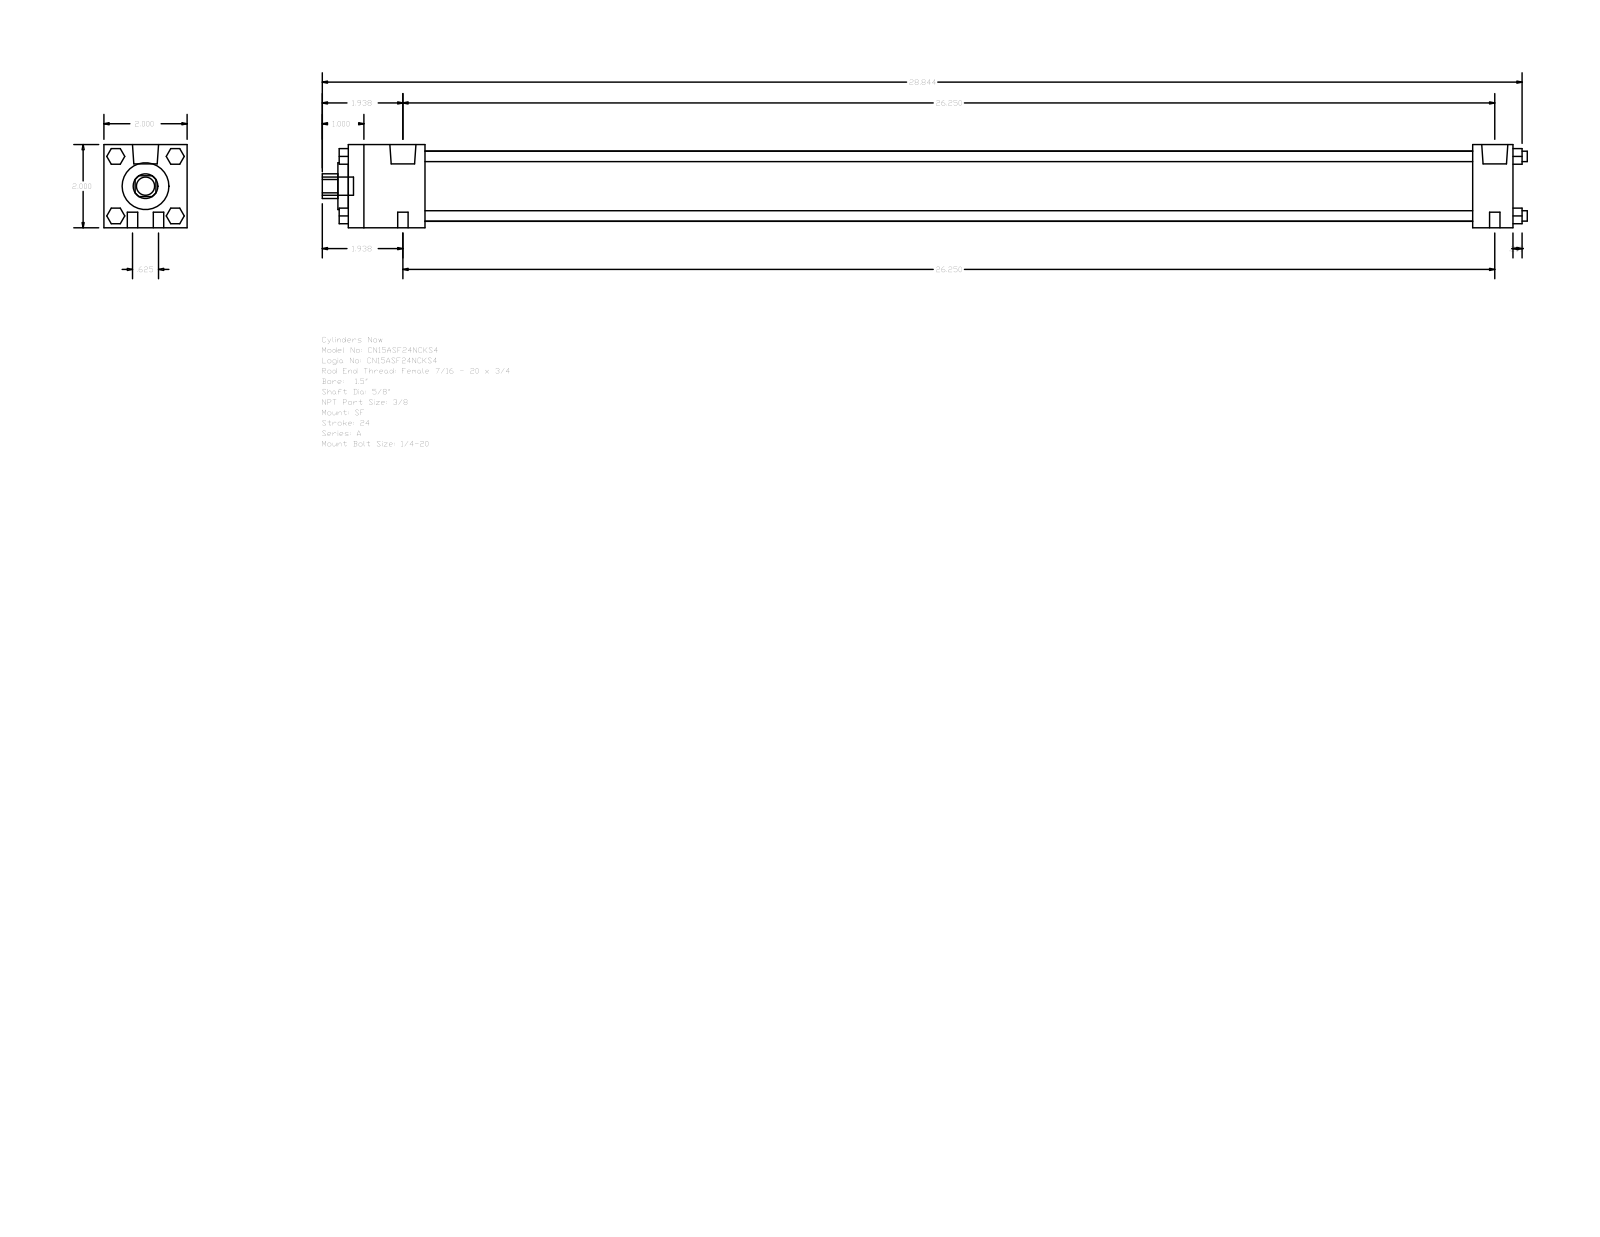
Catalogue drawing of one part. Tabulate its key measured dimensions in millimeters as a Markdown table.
| quantity | value |
| --- | --- |
| part name | A_SF__0150_0.625 |
| STEP written by | GSSL Pune (CONFIG_CONTROL_DESIGN) |
| units | millimeters |
| bodies | 0 solids, 124 faces (94 planar, 30 cylindrical, 0 other) |
| overall size | 735.81 × 50.8 × 50.8 |
| round holes (diameter × count) | 15.88 × 1, 28.57 × 1, 42.93 × 1 |
| round bosses / shafts (diameter × count) | 6.35 × 8, 15.93 × 2, 5.56 × 2, 11.11 × 1 |
| partial cylindrical surfaces (radius × count) | 7.54 × 1 |
| main face-to-face distances | 50.8, 711.2, 46.83, 686.59, 639.76, 664.37, 24.61, 9.52, 6.35, 53.18 |
